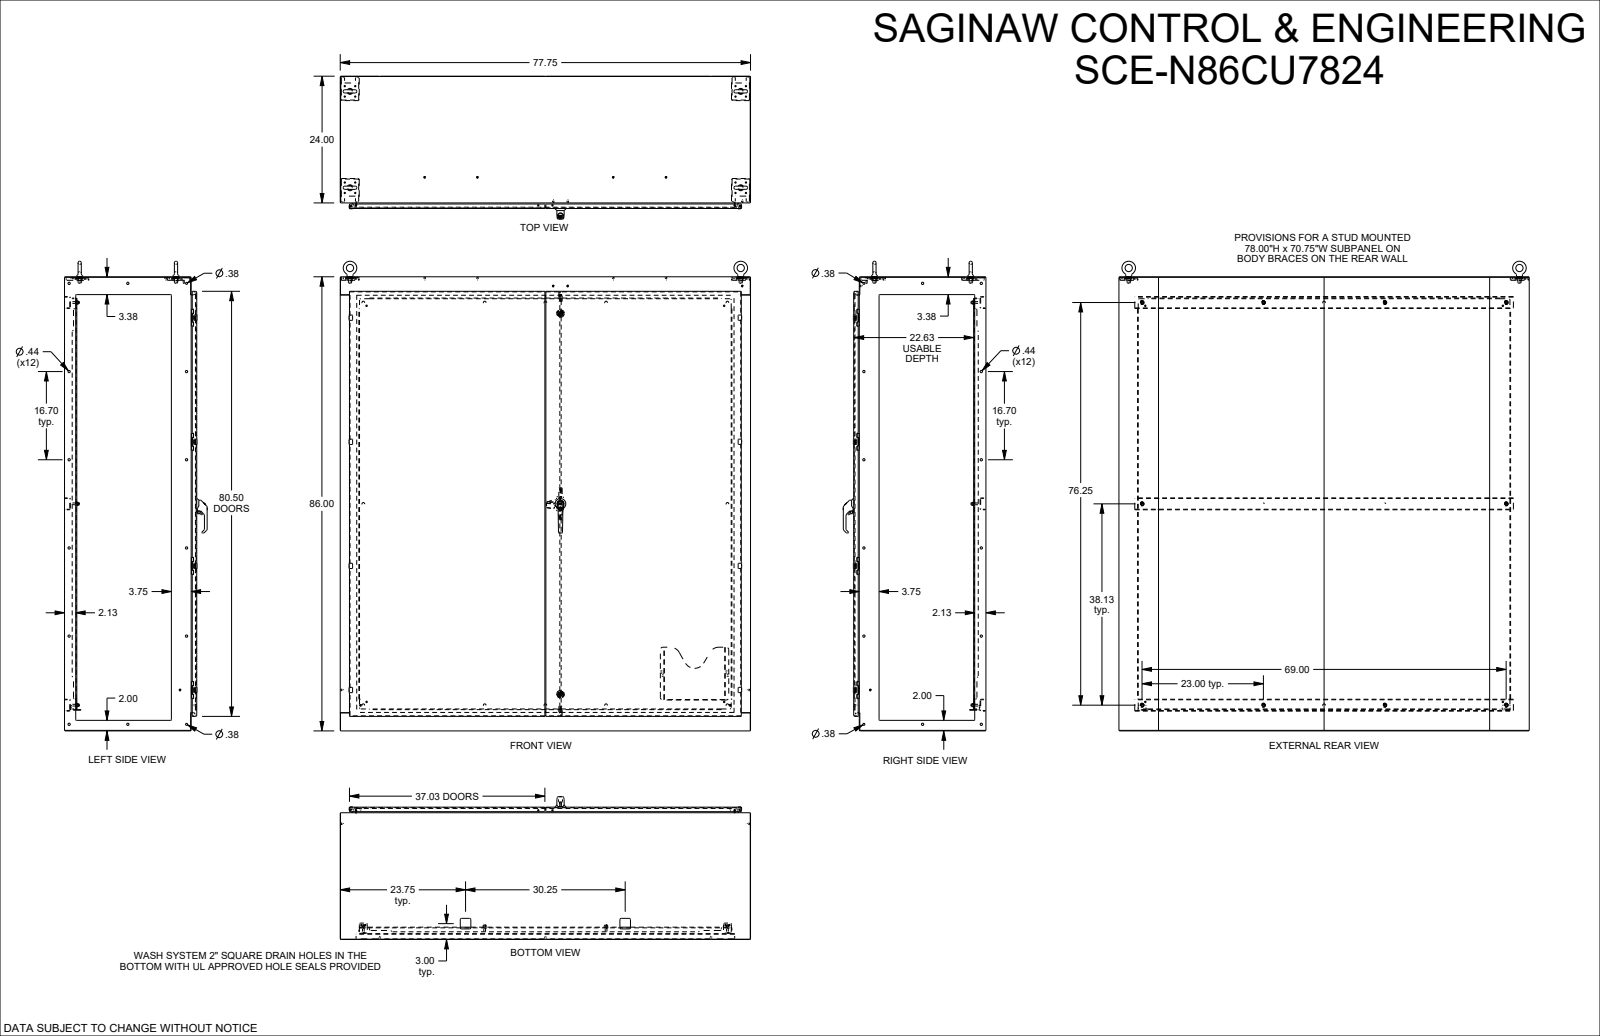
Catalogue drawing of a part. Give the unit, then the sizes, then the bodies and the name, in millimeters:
Units: millimetres
Overall size (bounding box): 2259.2 × 1974.9 × 687
Round holes (diameter × count): ⌀6.4 ×18, ⌀9.5 ×18, ⌀5.2 ×16, ⌀6.2 ×16, ⌀11.1 ×12, ⌀1 ×8, ⌀5.5 ×8, ⌀4.3 ×4, ⌀6.5 ×4, ⌀22.2 ×4, ⌀5.2 ×2, ⌀8.7 ×2
Round bosses / shafts (diameter × count): ⌀4.3 ×24, ⌀6.4 ×16, ⌀6.1 ×16, ⌀5 ×10, ⌀29.8 ×4, ⌀15.2 ×4, ⌀35.6 ×2, ⌀10.3 ×2
Partial cylindrical surfaces — rounded edges, fillets, slot ends (radius × count): R0.8 ×102, R0.4 ×90, R3.2 ×67, R4.2 ×38, R1.6 ×34, R1.6 ×34, R5.8 ×32, R2.5 ×31
Main face-to-face distances: 2.6, 633.8, 636.5, 631.2, 2181.8, 607, 26.9, 2184.4, 2179.1, 604.3
Hole centre spacings: 596.9, 50.3, 1193.8, 35.6, 1850.8, 424.2, 706.6, 1940.9
Volume: 35 610 000 mm³ · Surface area: 26 880 000 mm²
Bodies: 33 solids, 4726 faces (2152 planar, 1578 cylindrical, 996 other)
Part name (STEP PRODUCT): SCE-N86CU7824
STEP written by: SolidWorks 2023 (AUTOMOTIVE_DESIGN)
